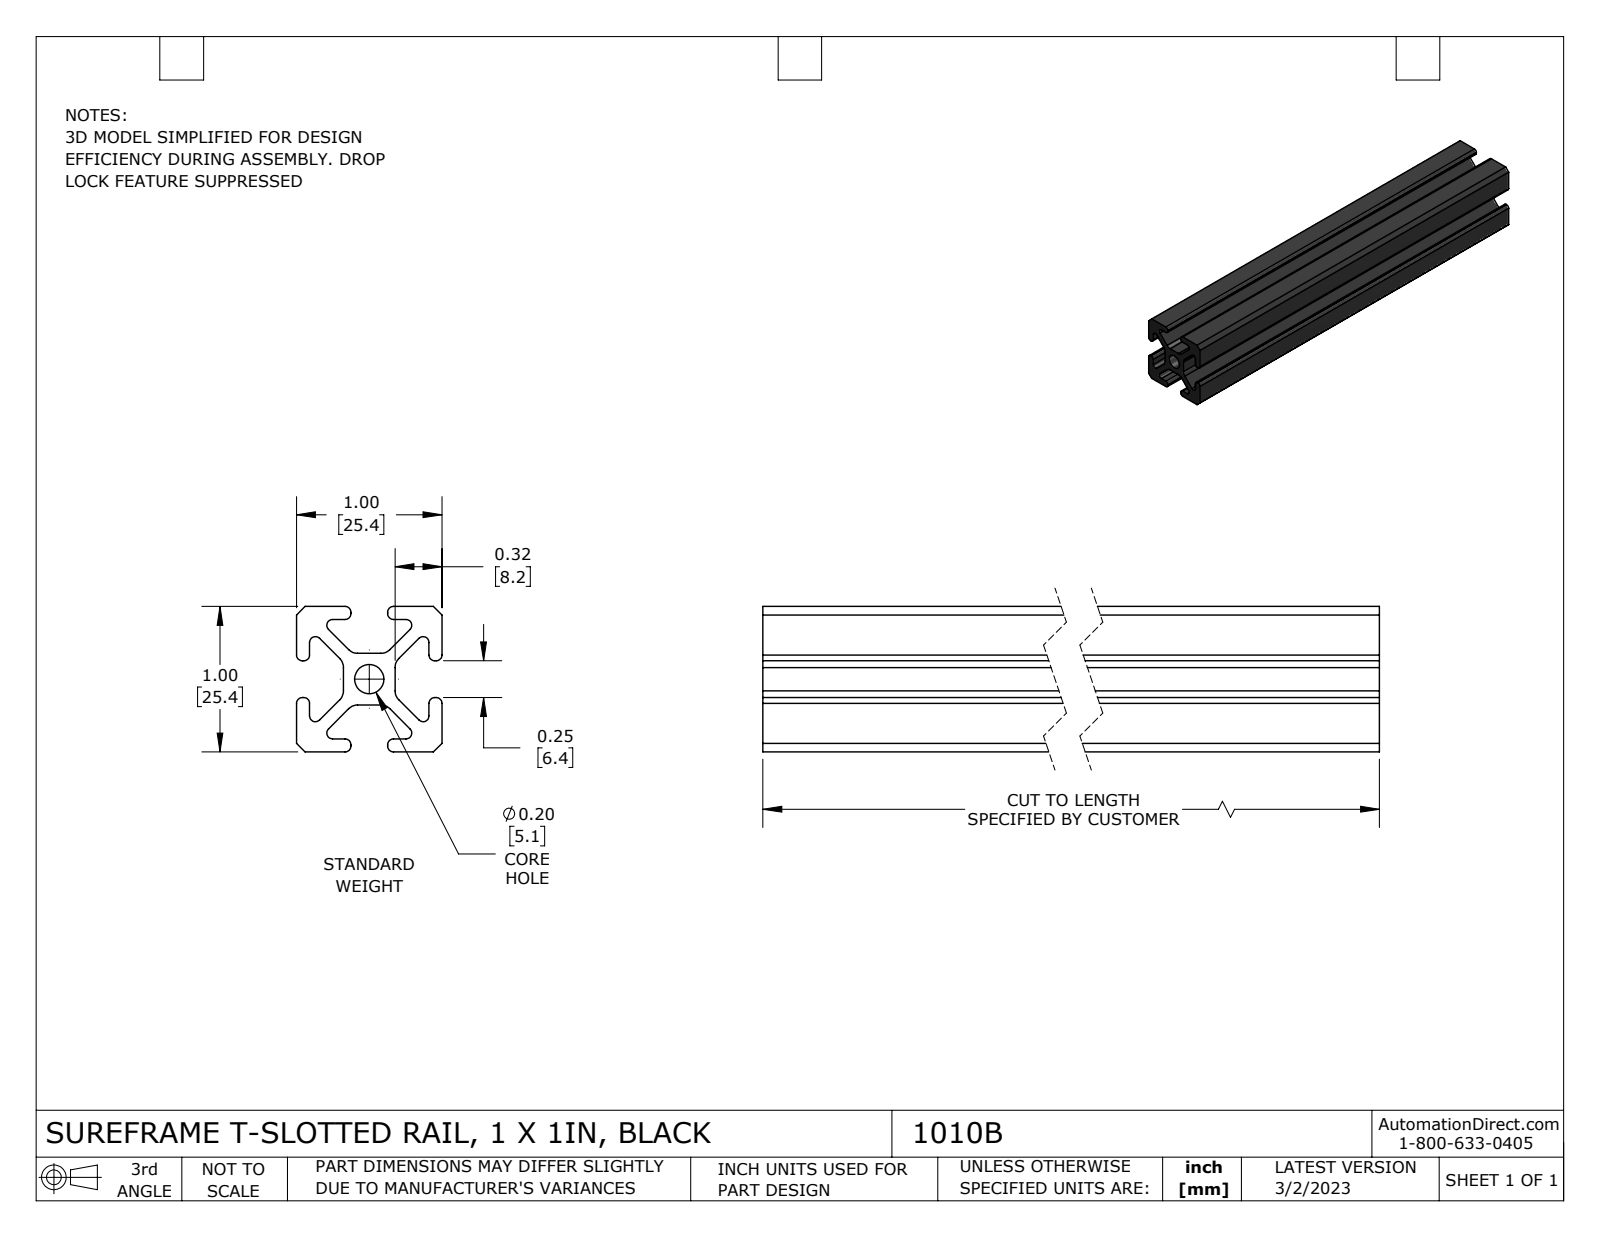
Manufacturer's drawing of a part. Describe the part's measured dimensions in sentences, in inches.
The part is named "1010B". Its 3-D file was written by "SolidWorks 2021 (CONFIG_CONTROL_DESIGN)". It is 1 solid with 80 faces: 42 planar, 38 cylindrical and 0 other. Overall it measures 6 by 1 by 1 inches. Its volume is 2.696 cubic inches and its surface area 51.59 square inches. Round holes: 1 of diameter 0.201. Partial cylindrical surfaces (rounded edges, fillets, slot ends): 24 of radius 0.04, 8 of radius 0.087. The main face-to-face distances are 1, 0.087, 0.09, 0.91, 0.322, 0.678, 0.233, 0.588, 0.82, 0.622.
